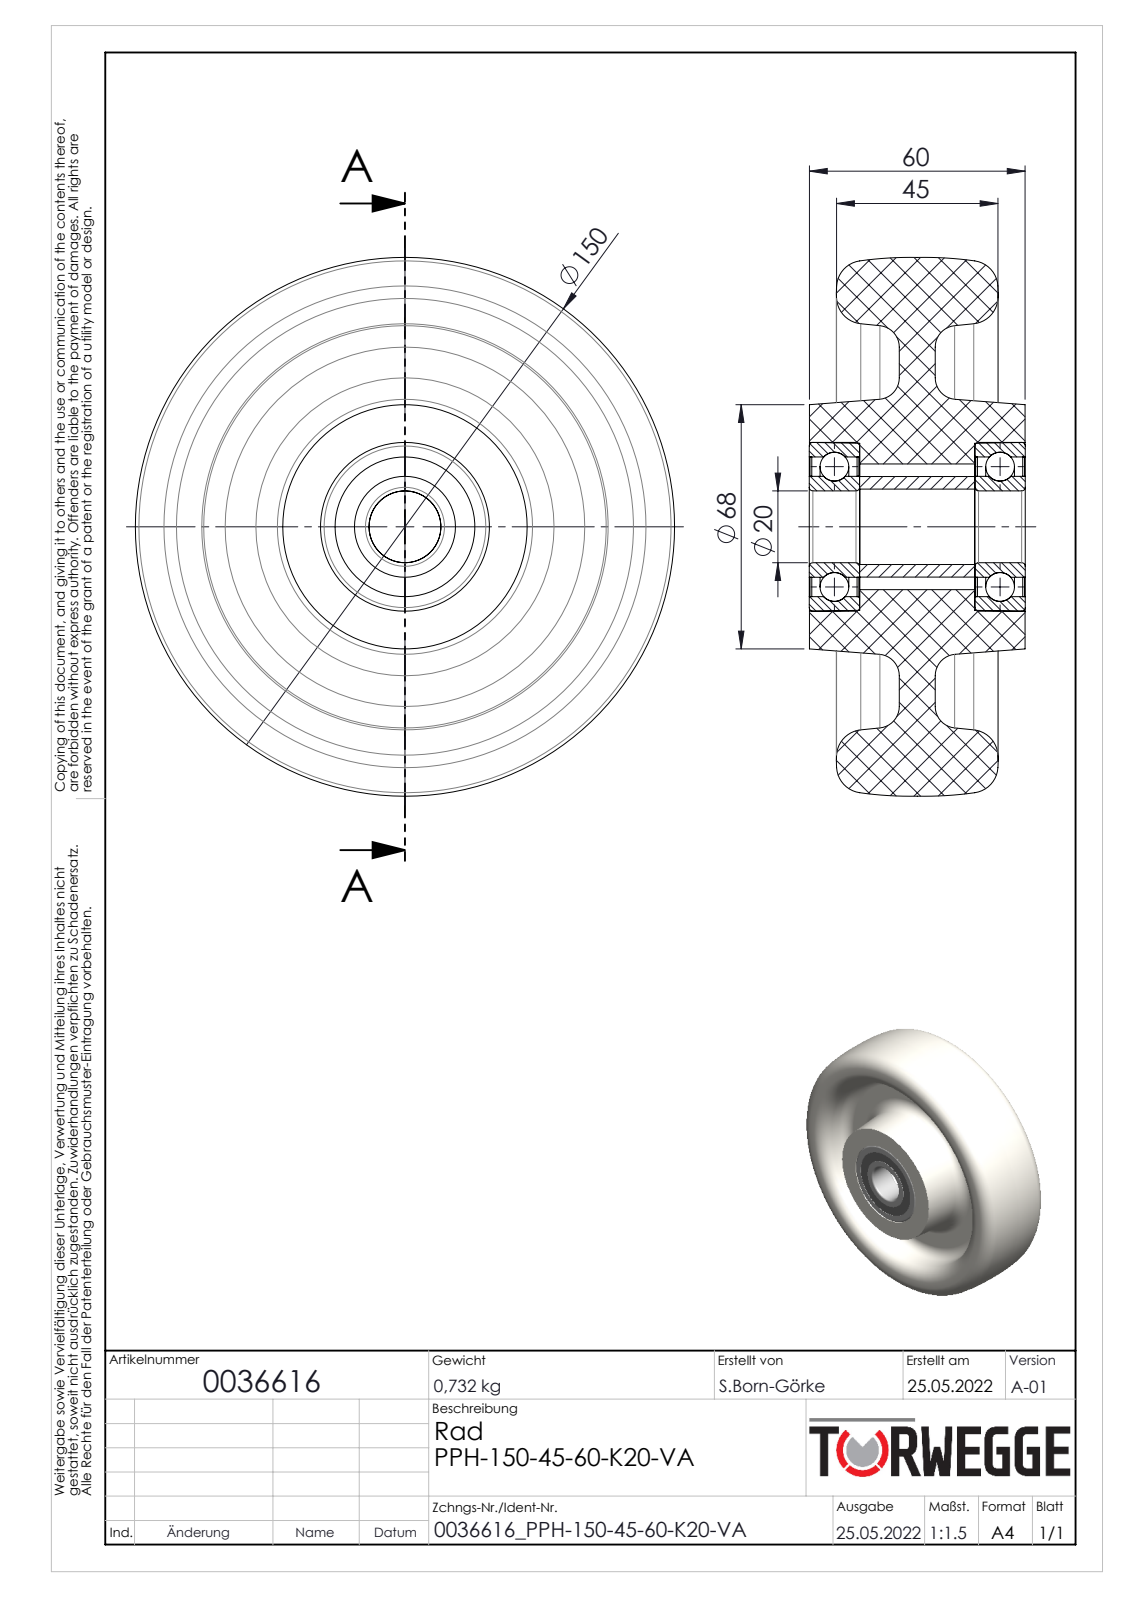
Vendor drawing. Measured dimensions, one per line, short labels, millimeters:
name: 0036616
written by: SolidWorks 2020 (AUTOMOTIVE_DESIGN)
unit: mm
bodies: 12 solids, 150 faces (24 planar, 46 cylindrical, 80 other)
size: 150.04 × 150.04 × 60.1
volume: 580 395 mm³; area: 106 249 mm²
holes: 1× ⌀20, 1× ⌀21, 1× ⌀28.1, 1× ⌀35, 1× ⌀38.9
bosses: 1× ⌀47, 1× ⌀28
face distances: 25, 35, 46.1, 46.05, 14, 10, 0.7, 13.3, 13.8, 0.5
